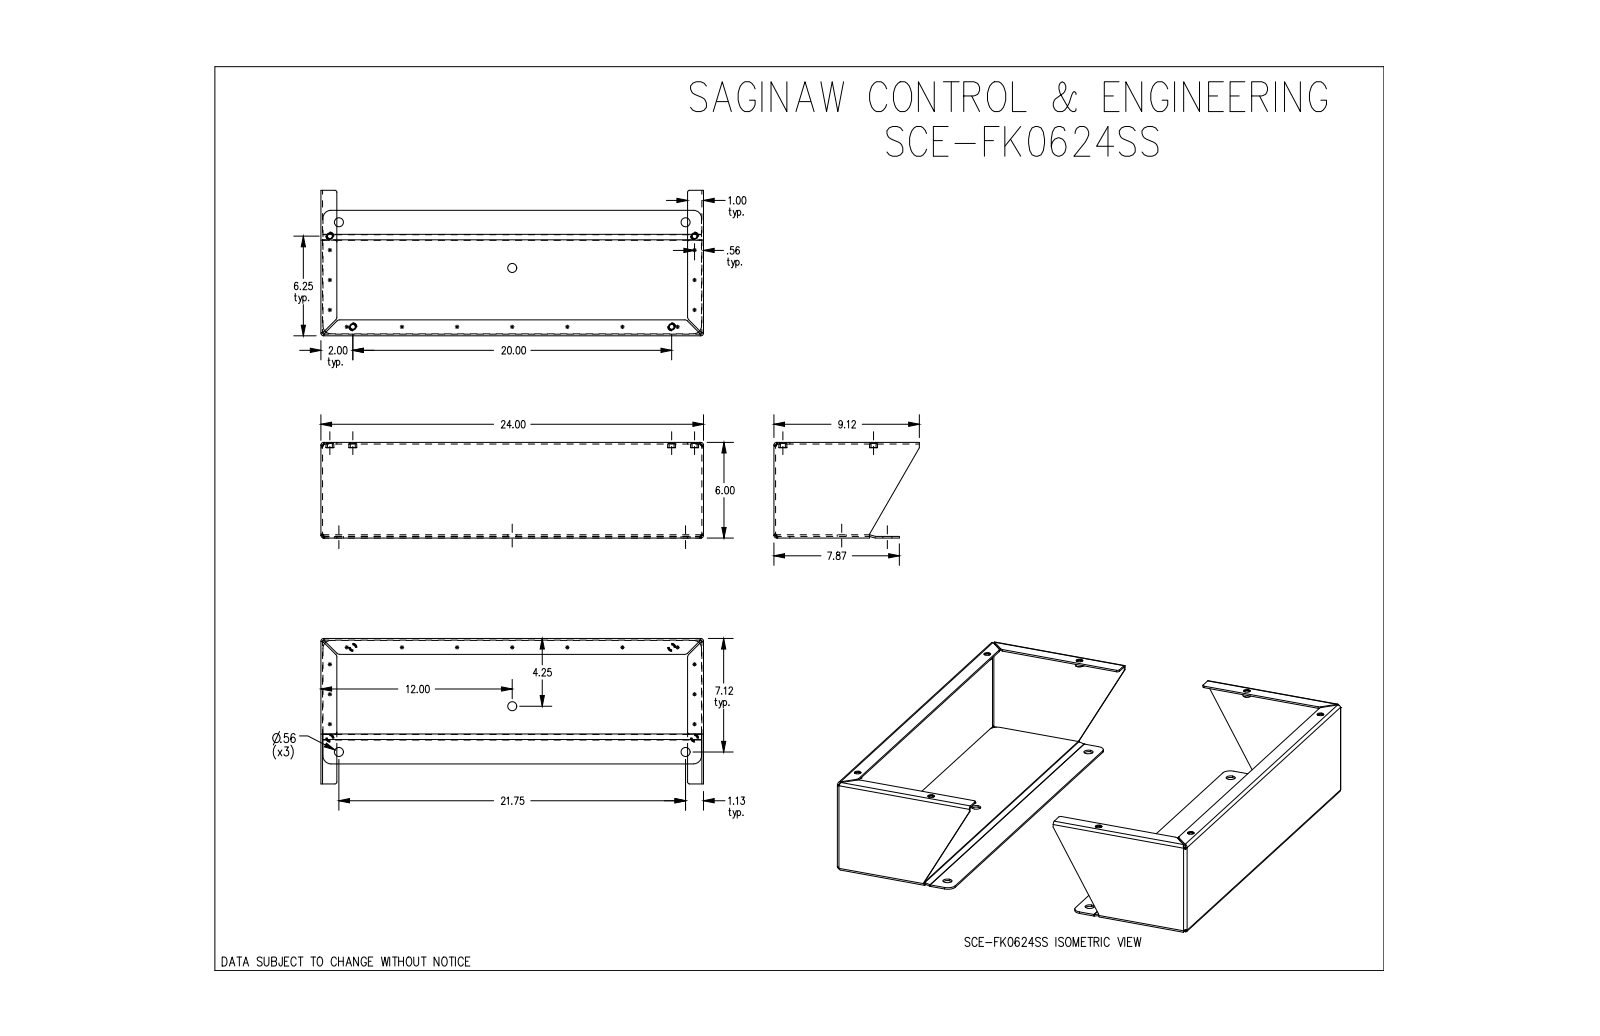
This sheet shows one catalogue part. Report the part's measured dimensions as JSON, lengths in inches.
{"part_name": "SCE-FK0624SS", "step_written_by": "SolidWorks 2019 (CONFIG_CONTROL_DESIGN)", "units": "inches", "bodies": {"solids": 12, "faces": 286, "planar": 120, "cylindrical": 110, "other": 56}, "overall_size": [24, 24, 6], "volume_in3": 99.56, "surface_area_in2": 1953, "round_holes": [[0.312, 8], [0.413, 8], [0.563, 6]], "round_bosses_or_shafts": [[0.5, 8], [0.412, 8]], "partial_cylinders_radius": [[0.166, 16], [0.062, 10], [0.063, 10], [0.125, 8], [0.22, 8], [0.5, 8]], "face_to_face_distances": [0.104, 23.896, 24, 23.792, 0.101, 5.893, 5.792, 5.896, 0.205, 5.789], "hole_center_spacings": [1.035, 5.866, 6.614, 10.646, 10.659, 11.611, 16.343, 17.247]}
